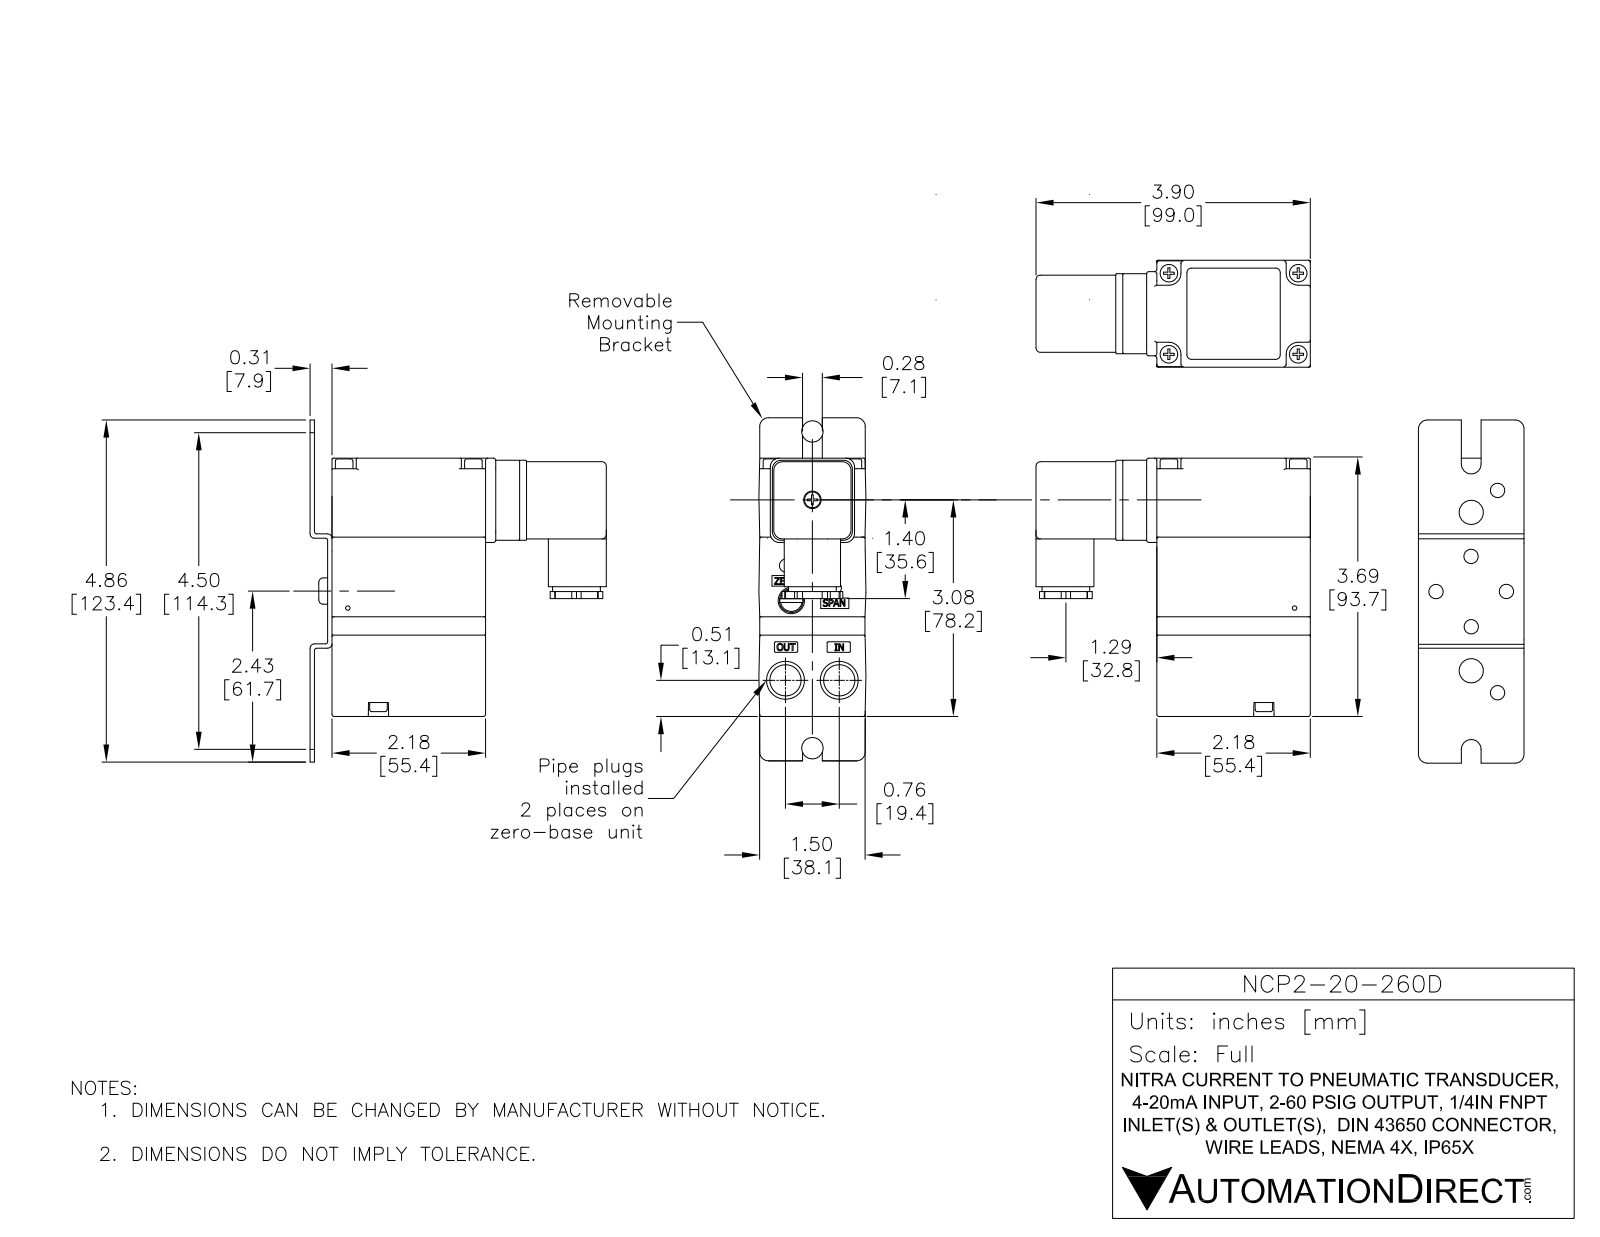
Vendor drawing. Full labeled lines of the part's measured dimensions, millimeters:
Part name (STEP PRODUCT): NCP2-20-260D
STEP written by: SolidWorks 2016 (AUTOMOTIVE_DESIGN)
Units: millimetres
Bodies: 5 solids, 1129 faces (622 planar, 321 cylindrical, 186 other)
Overall size (bounding box): 123.83 × 107.43 × 38.77
Volume: 223 787 mm³ · Surface area: 53 073 mm²
Round holes (diameter × count): ⌀5.16 ×6, ⌀3.37 ×3, ⌀3.18 ×2, ⌀3.3 ×2, ⌀4.8 ×2, ⌀8.73 ×2, ⌀11.38 ×2, ⌀1.59 ×1, ⌀3.17 ×1, ⌀6.35 ×1, ⌀7.37 ×1, ⌀11.43 ×1
Round bosses / shafts (diameter × count): ⌀6.6 ×4, ⌀6.35 ×3, ⌀7.49 ×2, ⌀20.32 ×1, ⌀18.32 ×1, ⌀16.18 ×1, ⌀11.43 ×1, ⌀8.66 ×1
Partial cylindrical surfaces — rounded edges, fillets, slot ends (radius × count): R0.76 ×56, R3.17 ×20, R0.5 ×17, R0.4 ×12, R1.47 ×6, R1.59 ×6, R0.79 ×4, R1.25 ×4
Main face-to-face distances: 1.59, 6.85, 8.44, 55.55, 37.35, 38.74, 1.39, 6.74, 8.33, 1.69
Hole centre spacings: 25.4, 33.68, 12.4, 17.74, 17.94, 18.41, 18.78, 21.29
